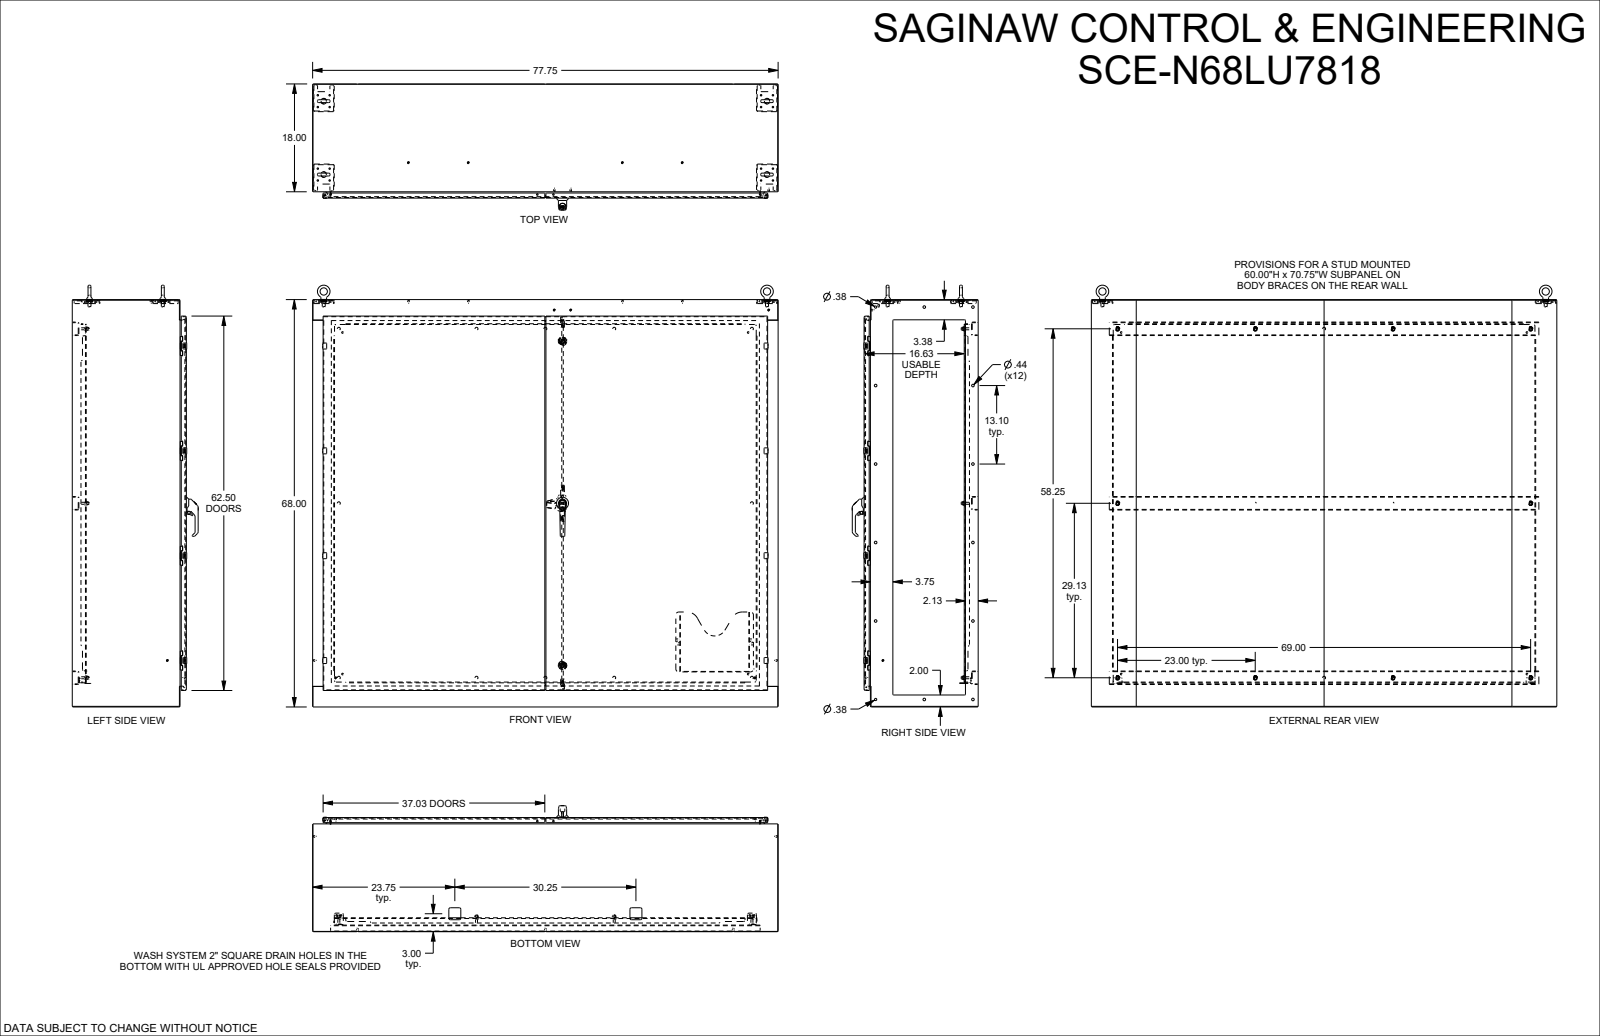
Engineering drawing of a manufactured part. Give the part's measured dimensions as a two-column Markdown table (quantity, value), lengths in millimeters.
| quantity | value |
| --- | --- |
| part name | SCE-N68LU7818 |
| STEP written by | SolidWorks 2023 (AUTOMOTIVE_DESIGN) |
| units | millimeters |
| bodies | 34 solids, 5109 faces (2418 planar, 1687 cylindrical, 1004 other) |
| overall size | 1974.9 × 1802 × 534.6 |
| volume | 29 580 000 mm³ |
| surface area | 22 330 000 mm² |
| round holes (diameter × count) | 6.4 × 19, 9.5 × 18, 6.2 × 16, 11.1 × 12, 1 × 8, 5.2 × 8, 5.2 × 8, 5.5 × 8, 4.3 × 4, 6.5 × 4, 22.2 × 4, 5.2 × 2 |
| round bosses / shafts (diameter × count) | 4.3 × 24, 6.4 × 16, 6.1 × 16, 16.4 × 12, 5 × 10, 29.8 × 4, 15.2 × 4, 35.6 × 2 |
| partial cylindrical surfaces (radius × count) | 0.8 × 102, 0.4 × 88, 3.2 × 67, 1.6 × 66, 1 × 41, 4.2 × 38, 5.8 × 32, 2.5 × 25 |
| main face-to-face distances | 2.6, 481.4, 478.8, 484.1, 1724.6, 454.6, 26.9, 1727.2, 1721.9, 25.4 |
| hole center spacings | 444.5, 50.3, 889, 1850.8, 35.6, 1900.6, 1902.5, 332.7 |
